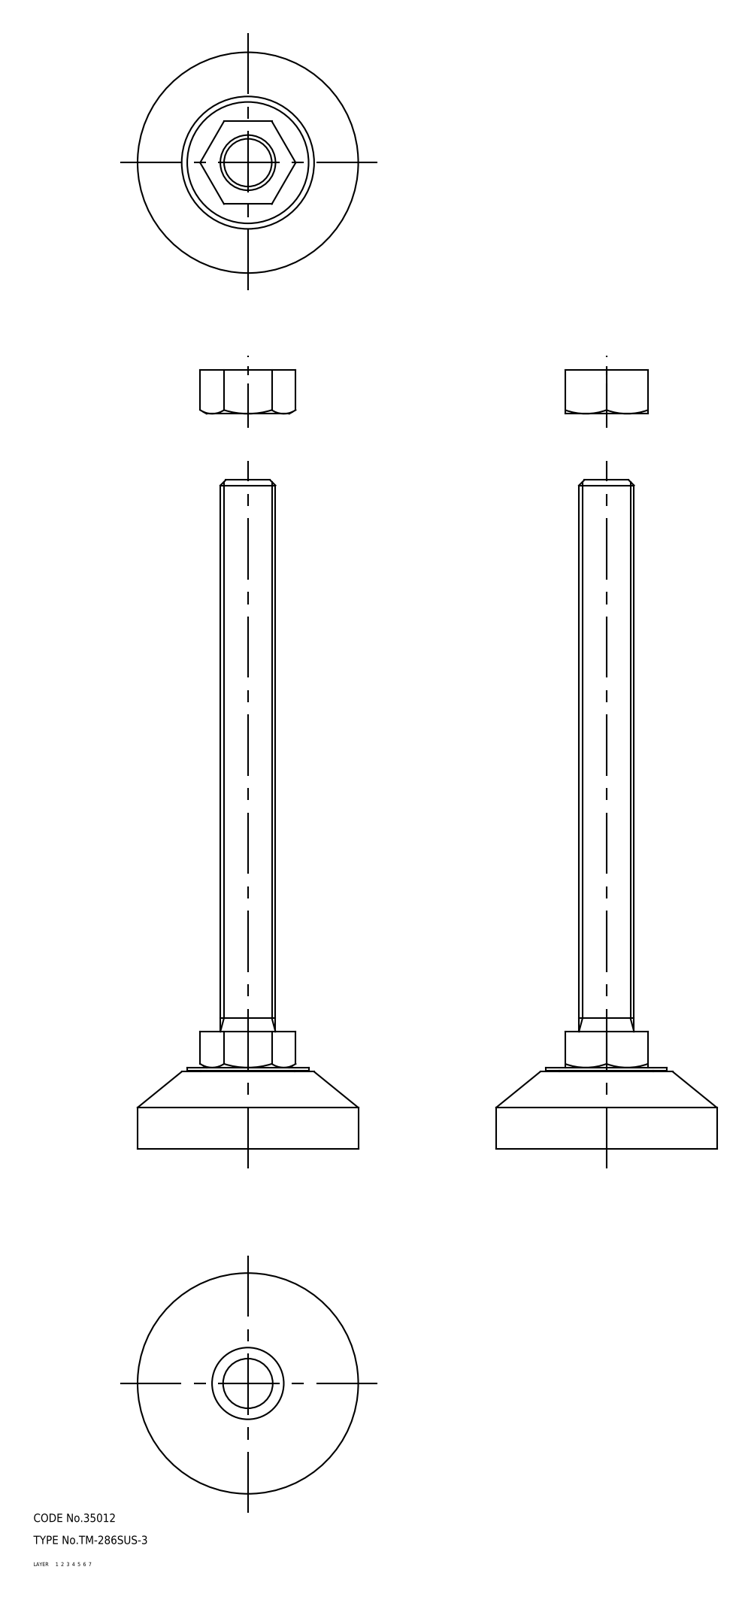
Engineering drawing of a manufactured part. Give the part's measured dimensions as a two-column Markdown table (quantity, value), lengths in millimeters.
| quantity | value |
| --- | --- |
| part name | 67111642; 67111655 |
| STEP written by | CADfix (AUTOMOTIVE_DESIGN) |
| units | millimeters |
| bodies | 2 solids, 52 faces (0 planar, 0 cylindrical, 52 other) |
| overall size | 242.5 × 80 × 80 |
| volume | 197 885 mm³ |
| surface area | 34 507 mm² |
